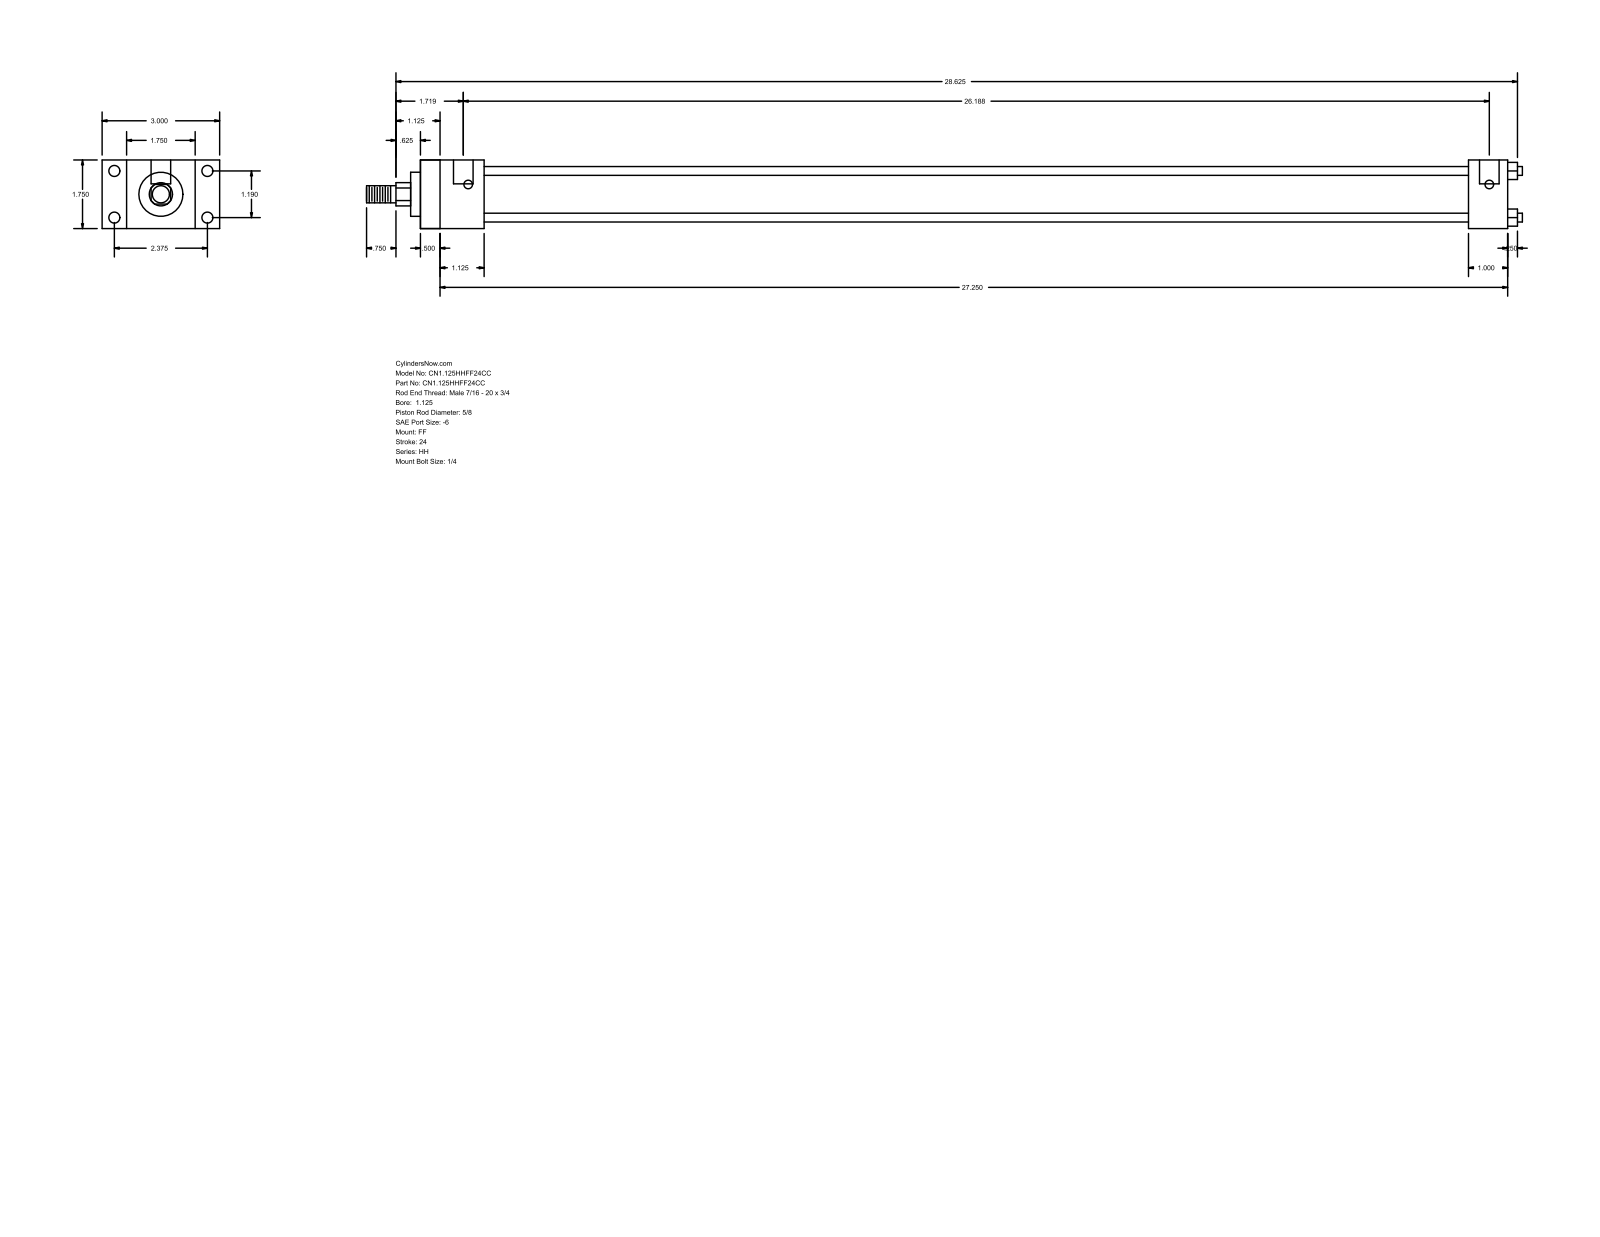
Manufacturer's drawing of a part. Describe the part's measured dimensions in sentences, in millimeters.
The part is named "HH_FF__0112_0.625". Its 3-D file was written by "GSSL Pune (CONFIG_CONTROL_DESIGN)". It is 0 solids with 92 faces: 64 planar, 28 cylindrical and 0 other. Overall it measures 749.3 by 76.2 by 44.45 millimeters. Round holes: 4 of diameter 5.56, 4 of diameter 7.14, 2 of diameter 12.7. Round bosses or shafts: 4 of diameter 5.71, 1 of diameter 34.92, 1 of diameter 28.57, 1 of diameter 15.88, 1 of diameter 11.11. Partial cylindrical surfaces (rounded edges, fillets, slot ends): 1 of radius 7.54. The main face-to-face distances are 44.46, 704.85, 12.69, 692.16, 15.87, 28.58, 60.33, 25.4, 41.27, 679.45. The hole center spacings are 30.22, 60.32, 67.47, 661.99, 3.17, 665.16.
